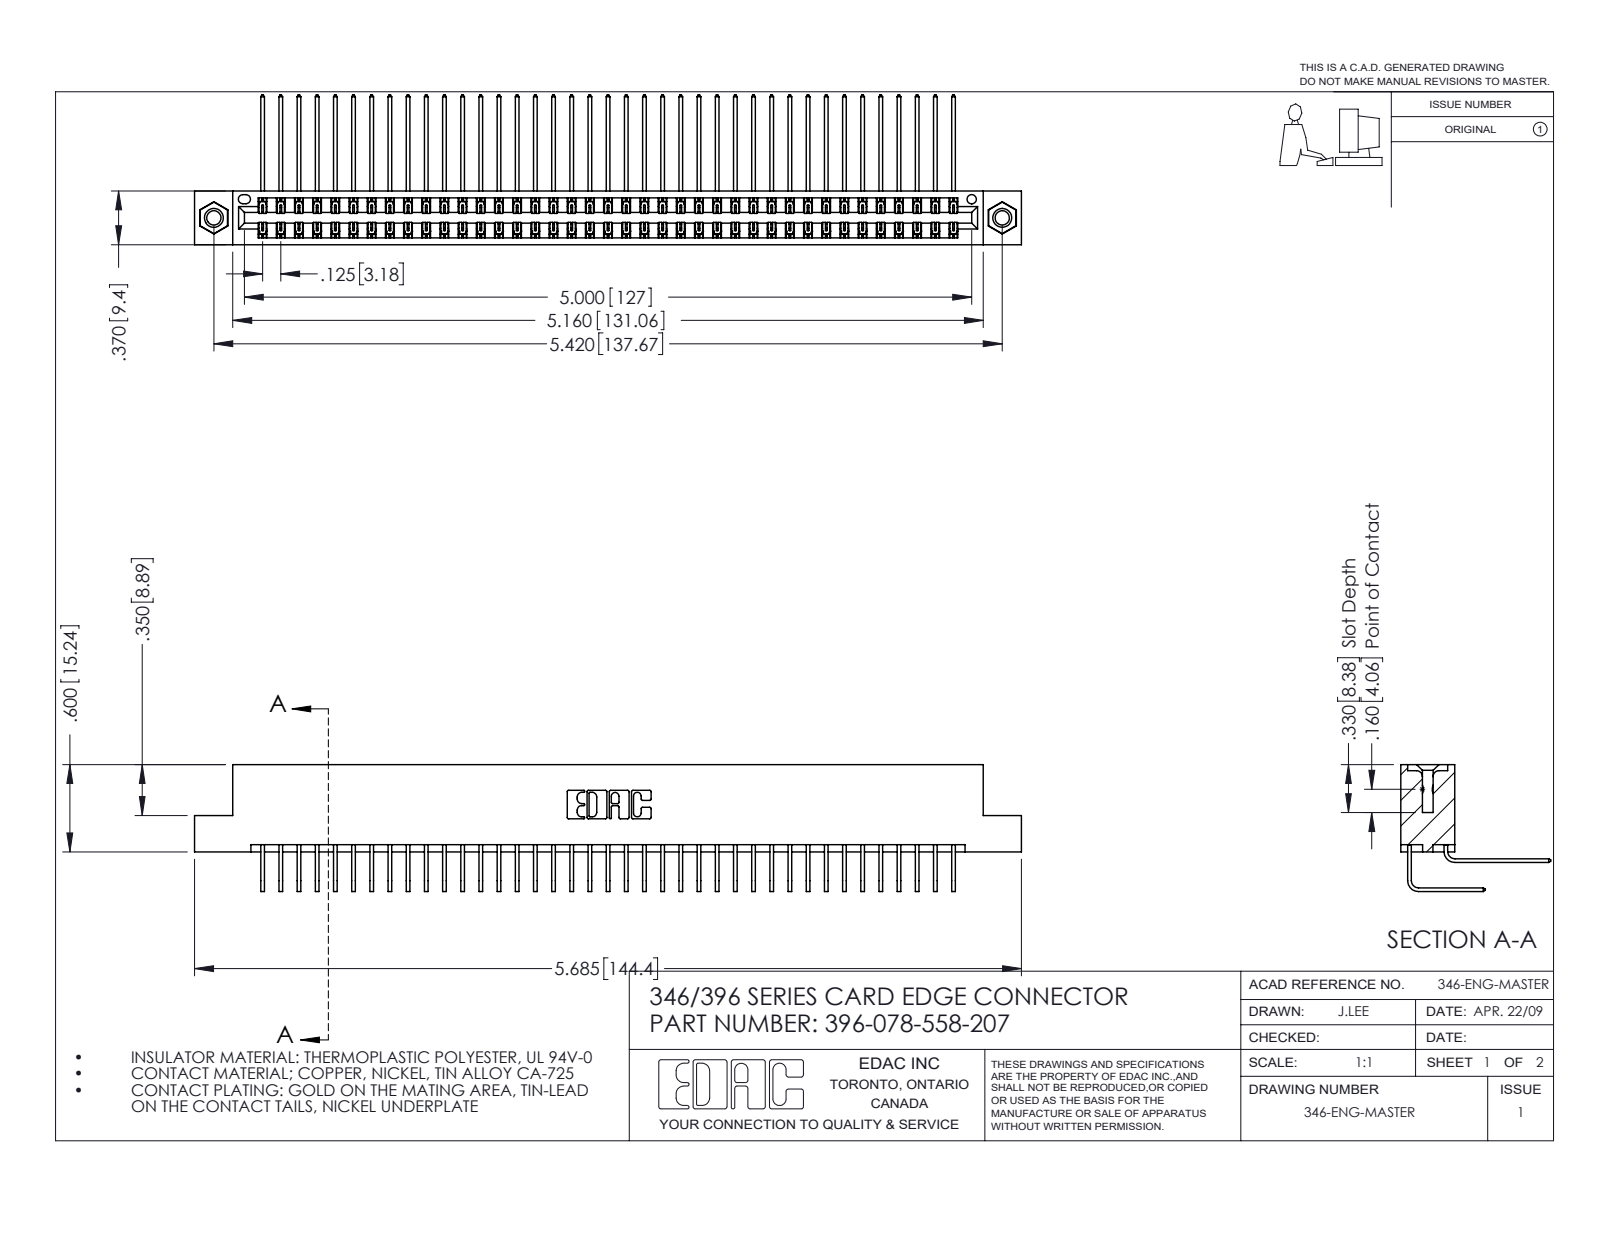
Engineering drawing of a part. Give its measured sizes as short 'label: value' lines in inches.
name: 345-250-001_345-250-005-103; 345-292-001_558 Tail - 2; 345-292-001_558 559 Tail - 1; 346 Part_Flush Mounting Lugs - 0.156 Dia-TI (+1 more)
written by: SolidWorks 2016 (CONFIG_CONTROL_DESIGN)
unit: in
bodies: 81 solids, 4394 faces (2994 planar, 1384 cylindrical, 16 other)
size: 5.685 × 1.03 × 0.873
volume: 0.884 in³; area: 34.21 in²
holes: 2× ⌀0.098, 2× ⌀0.125, 2× ⌀0.156, 1× ⌀0.064
bosses: 2× ⌀0.155
rounds: 117× R0.006, 22× R0.01, 6× R0.007, 6× R0.031, 3× R0.026, 2× R0.014, 2× R0.022, 2× R0.024
face distances: 0.048, 0.322, 0.025, 0.37, 0.25, 0.072, 0.298, 0.275, 0.148, 0.222
hole spacings: 0.246, 5.211, 5.42
